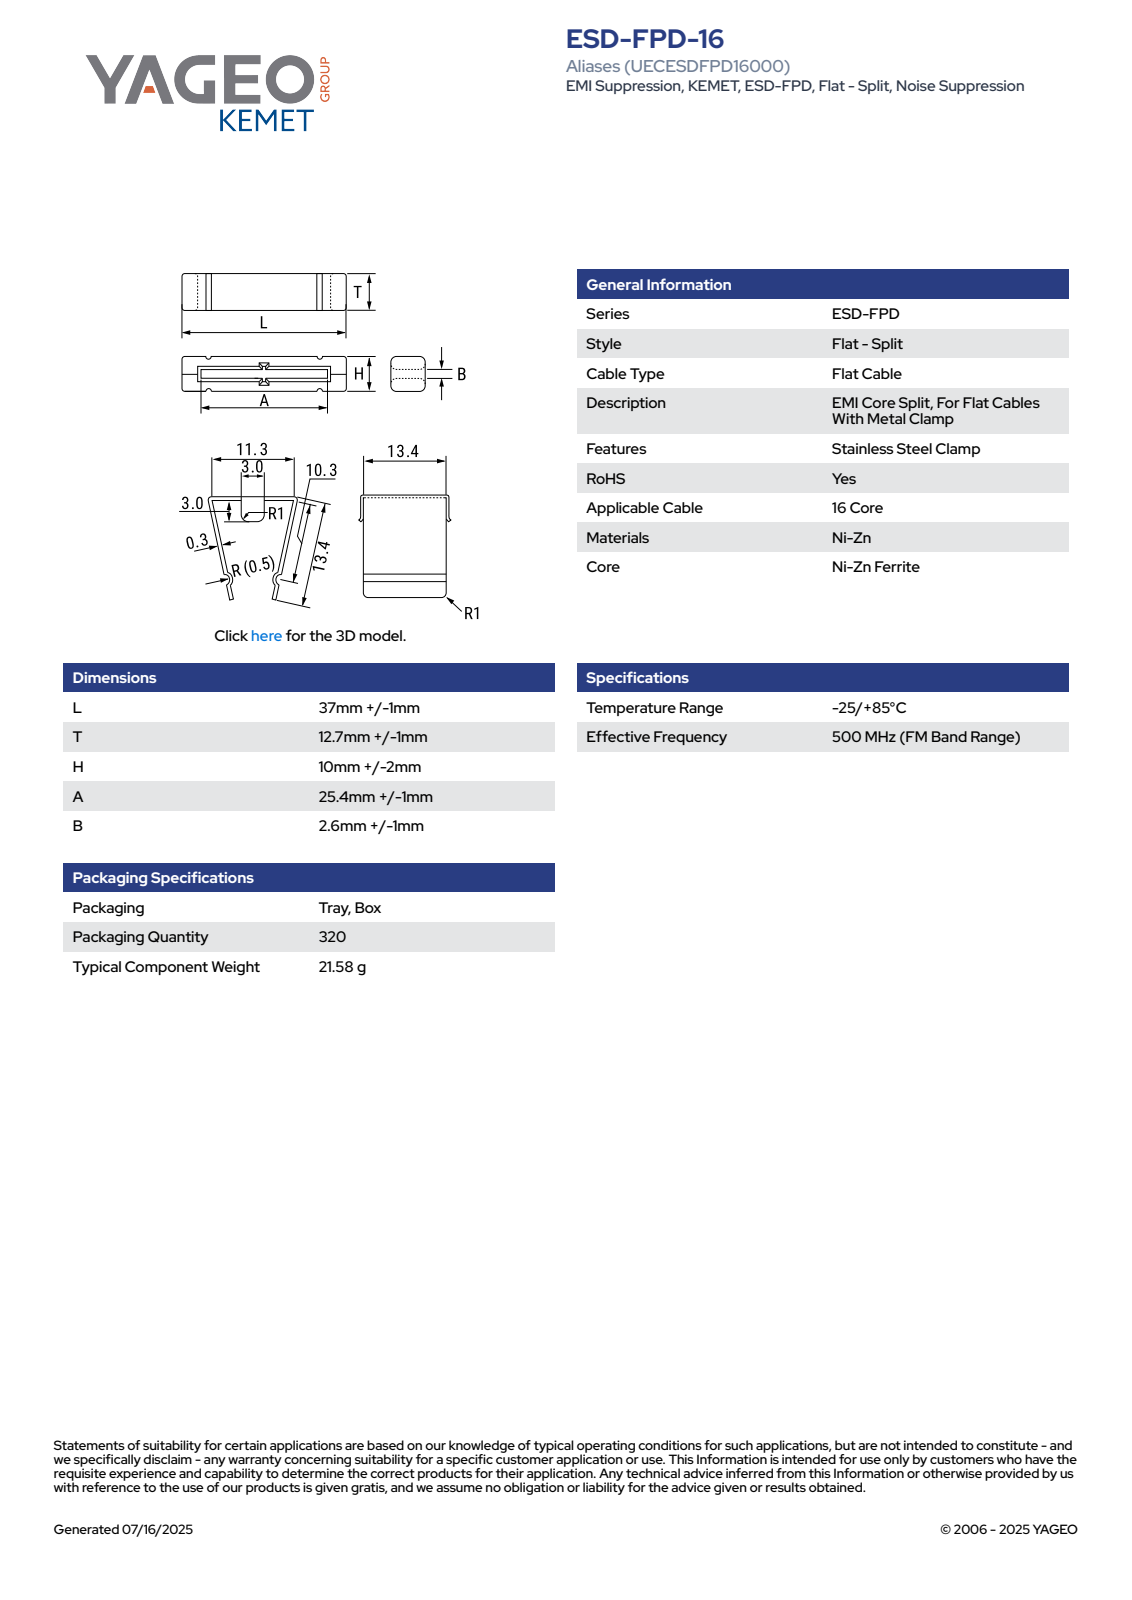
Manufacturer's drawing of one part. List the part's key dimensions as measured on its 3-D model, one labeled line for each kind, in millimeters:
Part name (STEP PRODUCT): EC_FPD_L38T13.7H12A25.4B2.6
STEP written by: SolidWorks 2021 (AUTOMOTIVE_DESIGN)
Units: millimetres
Bodies: 4 solids, 91 faces (79 planar, 12 cylindrical, 0 other)
Overall size (bounding box): 38 × 12.7 × 12
Volume: 4 911 mm³ · Surface area: 2 741 mm²
Partial cylindrical surfaces — rounded edges, fillets, slot ends (radius × count): R0.5 ×8, R0.62 ×4
Main face-to-face distances: 4.7, 7.3, 12, 12.7, 2.6, 38, 6.3, 31.7, 16.76, 25.4
